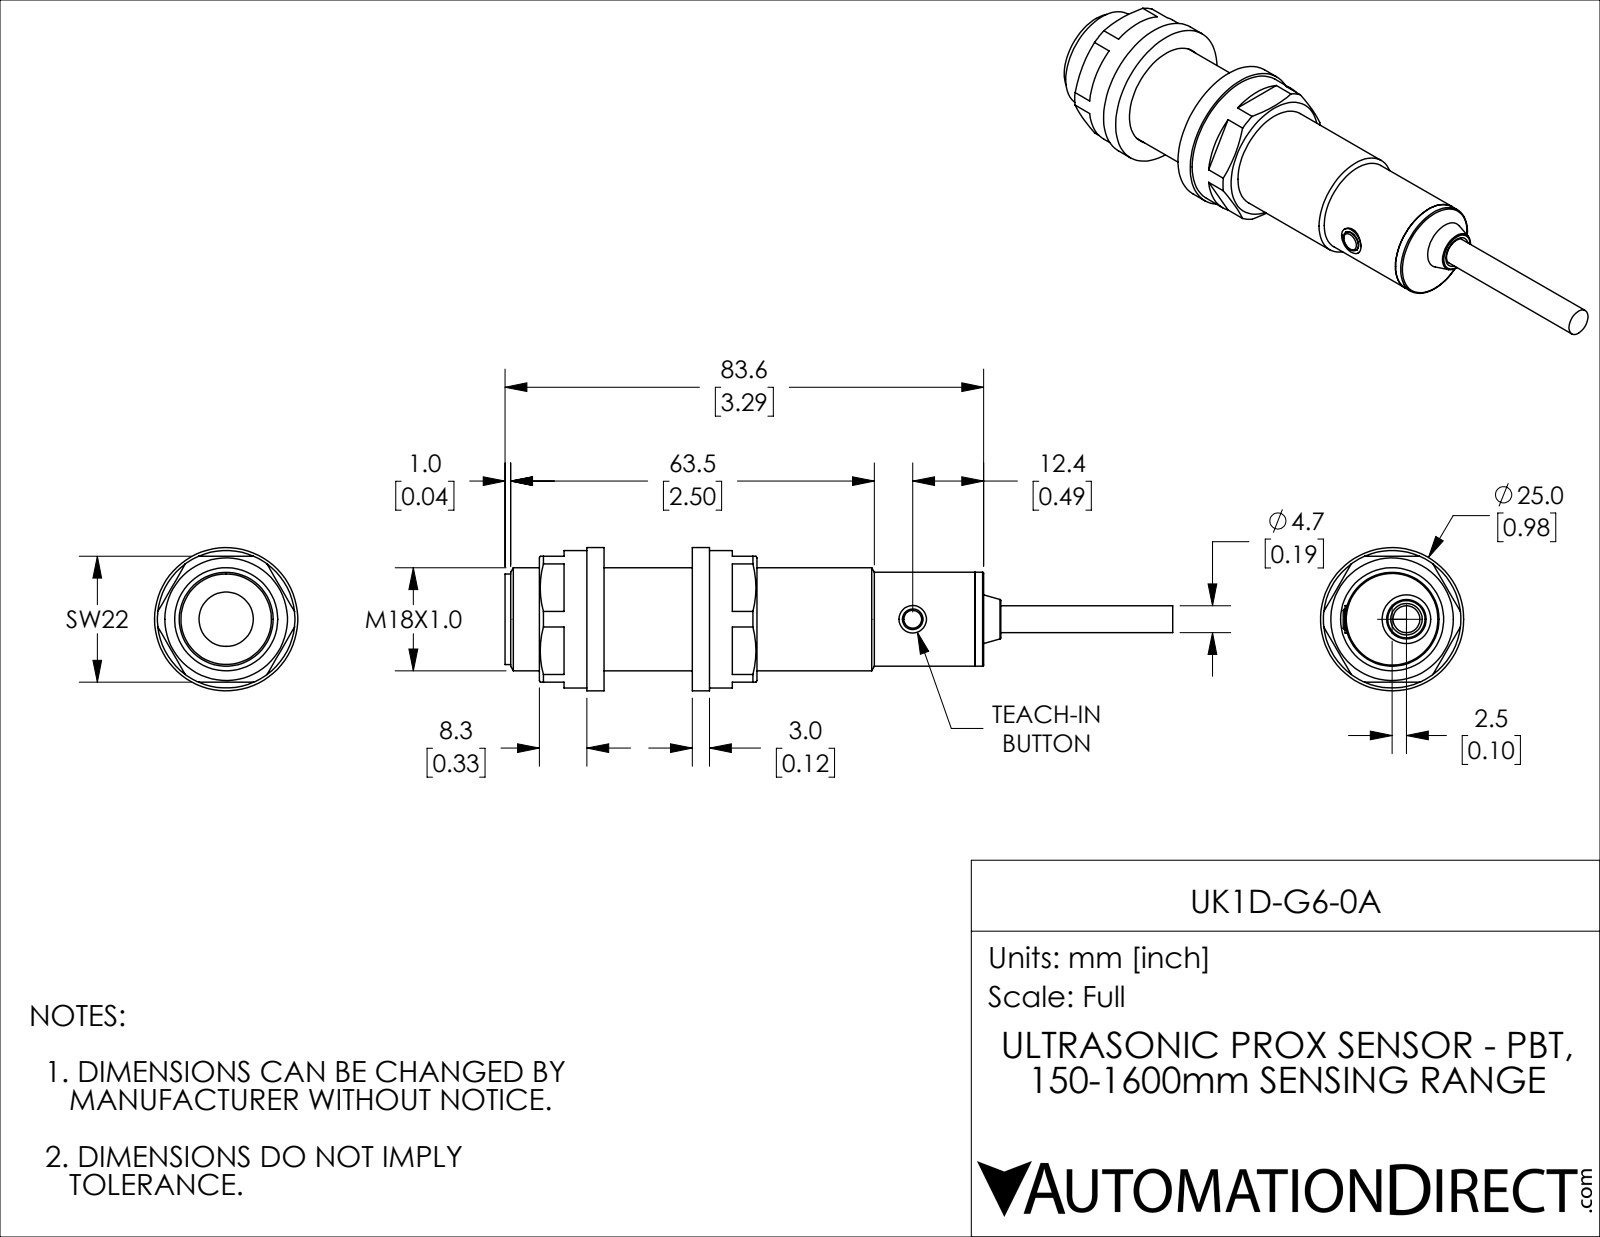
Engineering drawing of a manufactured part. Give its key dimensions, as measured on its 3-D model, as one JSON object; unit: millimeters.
{"part_name": "UK1D-G6-0A", "step_written_by": "SolidWorks 2018 (AUTOMOTIVE_DESIGN)", "units": "millimeters", "bodies": {"solids": 10, "faces": 107, "planar": 49, "cylindrical": 40, "other": 18}, "overall_size": [116.6, 25, 25], "volume_mm3": 25220, "surface_area_mm2": 11419, "round_holes": [[4.7, 2], [3.6, 1], [9.5, 1], [18, 1], [18.2, 1]], "round_bosses_or_shafts": [[25, 1], [24, 1], [16.4, 1], [15.8, 1], [5.4, 1], [4.8, 1]], "face_to_face_distances": [3, 18.4, 21.4, 67.8, 46.4, 13.3, 34.7, 81.1, 16.3, 64.8], "hole_center_spacings": [2.5]}
